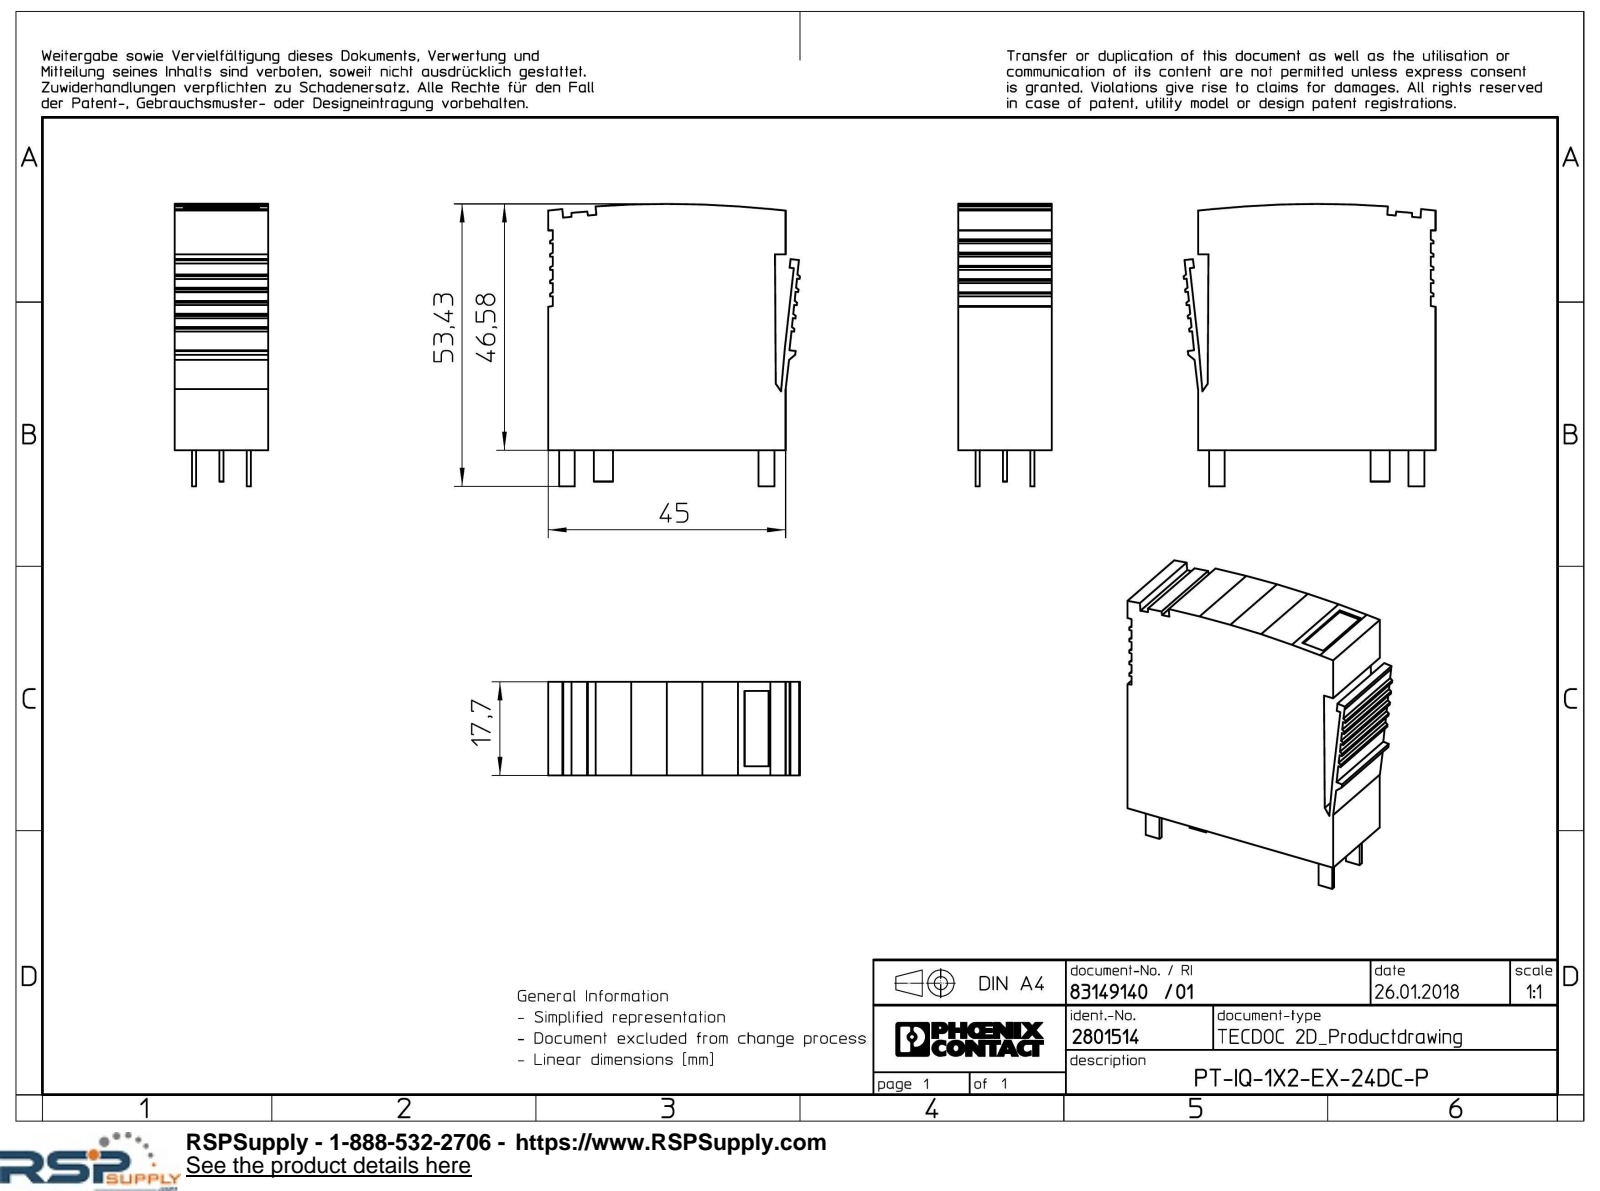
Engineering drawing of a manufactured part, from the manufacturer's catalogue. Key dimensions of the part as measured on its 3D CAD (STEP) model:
Part name (STEP PRODUCT): PT_IQ_3...P-select
STEP written by: Creo Elements/Direct Modeling 20.1A 29-Sep-2018 (C) Parametric Technology GmbH (AUTOMOTIVE_DESIGN)
Units: millimetres
Bodies: 1 solid, 154 faces (148 planar, 6 cylindrical, 0 other)
Overall size (bounding box): 53.42 × 47.71 × 17.7
Volume: 35 037 mm³ · Surface area: 9 408 mm²
Partial cylindrical surfaces — rounded edges, fillets, slot ends (radius × count): R0.3 ×4, R1.48 ×2
Main face-to-face distances: 17.7, 45, 0.9, 44.1, 1.1, 16.6, 0.8, 5.05, 12.65, 6.34
